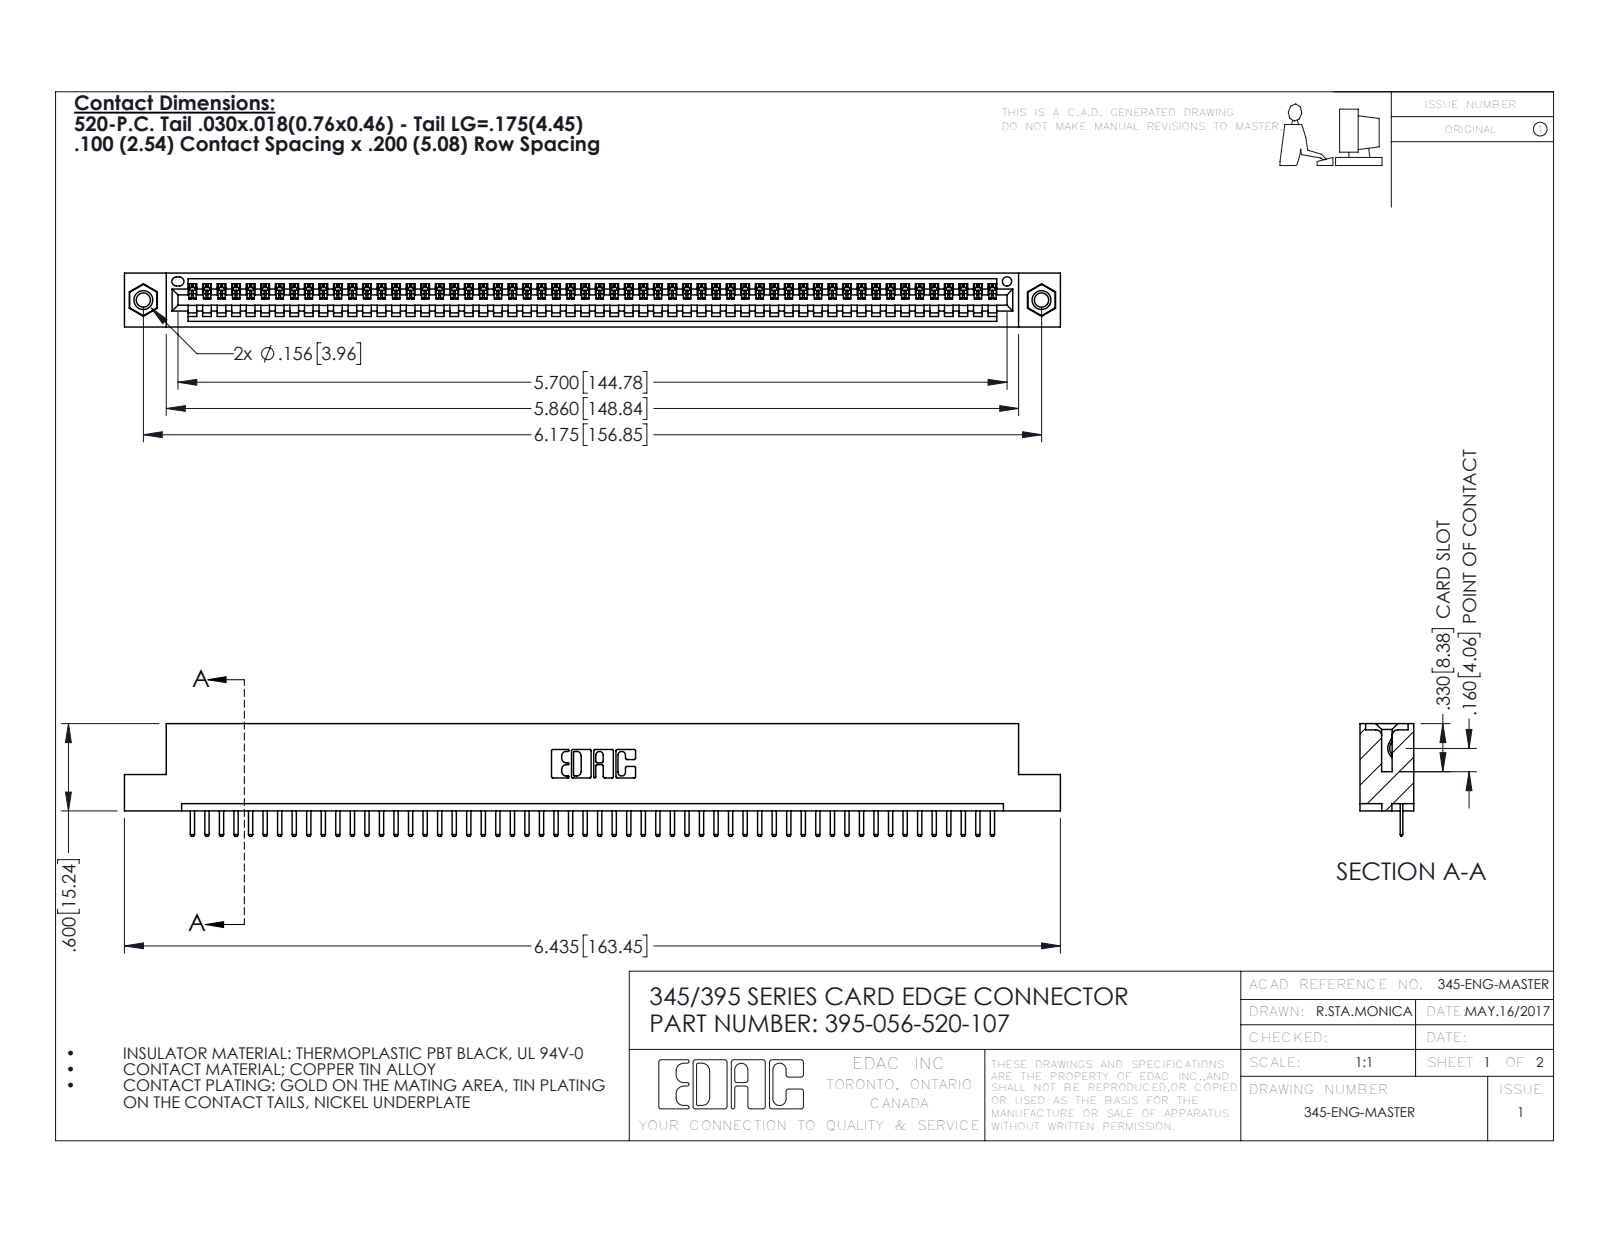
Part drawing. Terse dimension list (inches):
name: 345-292-001_345-293-120; 395-056-520-107; 345 Part_Flush Mounting Lugs - 0.156 Dia-TI; 345-250-001_345-250-005-103
written by: SolidWorks 2016 (CONFIG_CONTROL_DESIGN)
unit: in
bodies: 59 solids, 3658 faces (2464 planar, 1178 cylindrical, 16 other)
size: 6.435 × 0.775 × 0.37
volume: 0.944 in³; area: 31.38 in²
holes: 2× ⌀0.098, 2× ⌀0.125, 2× ⌀0.156, 1× ⌀0.064
bosses: 2× ⌀0.155
rounds: 114× R0.01, 112× R0.006, 22× R0.01, 6× R0.007, 6× R0.031, 3× R0.026, 2× R0.031, 2× R0.04
face distances: 0.072, 0.298, 0.37, 0.2, 0.098, 0.272, 0.025, 0.225, 0.072, 0.149
hole spacings: 0.27, 5.939, 6.175
